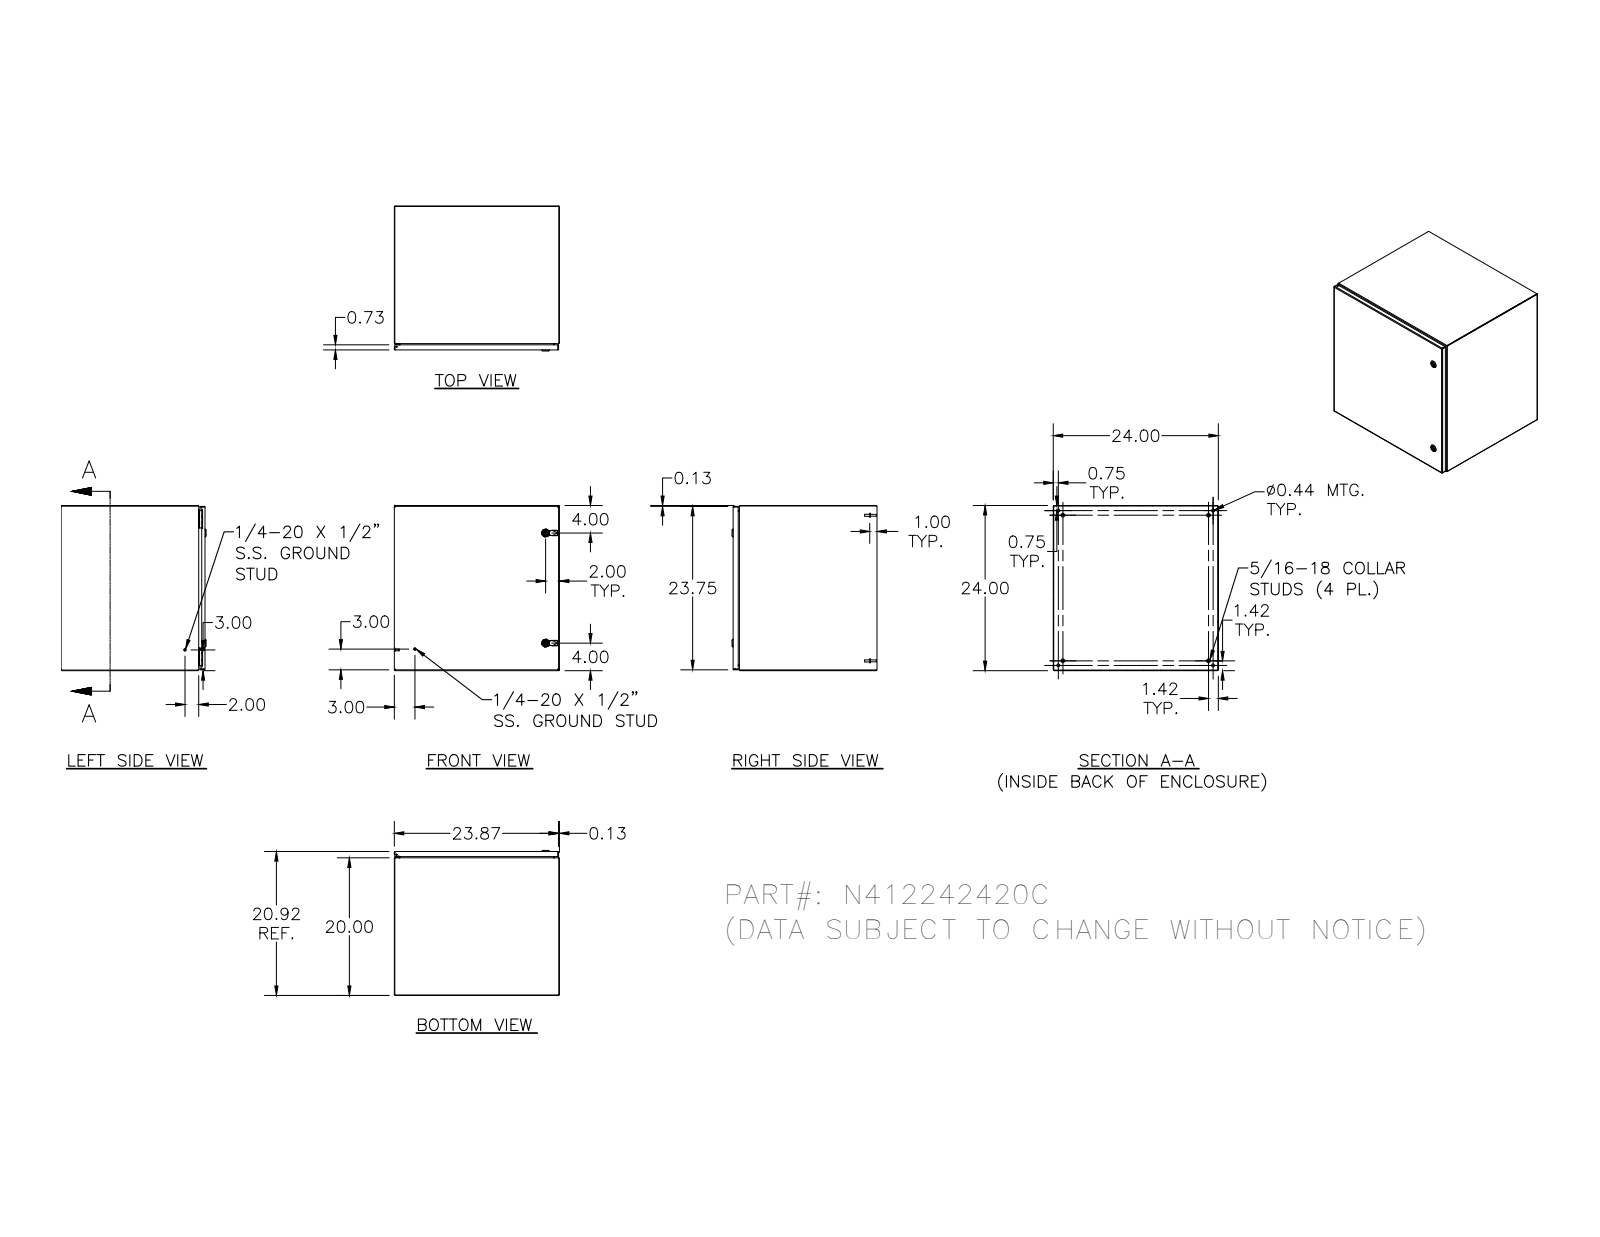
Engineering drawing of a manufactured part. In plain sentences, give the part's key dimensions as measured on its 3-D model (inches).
The part is named "N412242420C". Its 3-D file was written by "SolidWorks 2018 (AUTOMOTIVE_DESIGN)". It is 42 solids with 1786 faces: 702 planar, 660 cylindrical and 424 other. Overall it measures 24 by 24 by 21.075 inches. Its volume is 241.4 cubic inches and its surface area 6 556 square inches. Round holes: 5 of diameter 0.188, 4 of diameter 0.093, 4 of diameter 0.152, 4 of diameter 0.167, 4 of diameter 0.172, 4 of diameter 0.438, 2 of diameter 0.156, 2 of diameter 0.197, 2 of diameter 0.315, 2 of diameter 0.394, 2 of diameter 0.402, 2 of diameter 0.634. Round bosses or shafts: 10 of diameter 0.25, 4 of diameter 0.563, 4 of diameter 0.36, 4 of diameter 0.32, 4 of diameter 0.3, 4 of diameter 0.275, 4 of diameter 0.256, 4 of diameter 0.164. Partial cylindrical surfaces (rounded edges, fillets, slot ends): 54 of radius 0.012, 28 of radius 0.031, 26 of radius 0.05, 23 of radius 0.02, 18 of radius 0.016, 18 of radius 0.105, 16 of radius 0.125, 8 of radius 0.032. The main face-to-face distances are 0.074, 23.926, 20.843, 23.852, 24, 20.769, 20.917, 19.926, 0.917, 0.739. The hole center spacings are 20.004, 22.5, 0.5, 0.656, 0.66, 0.984, 1.615, 1.618.
